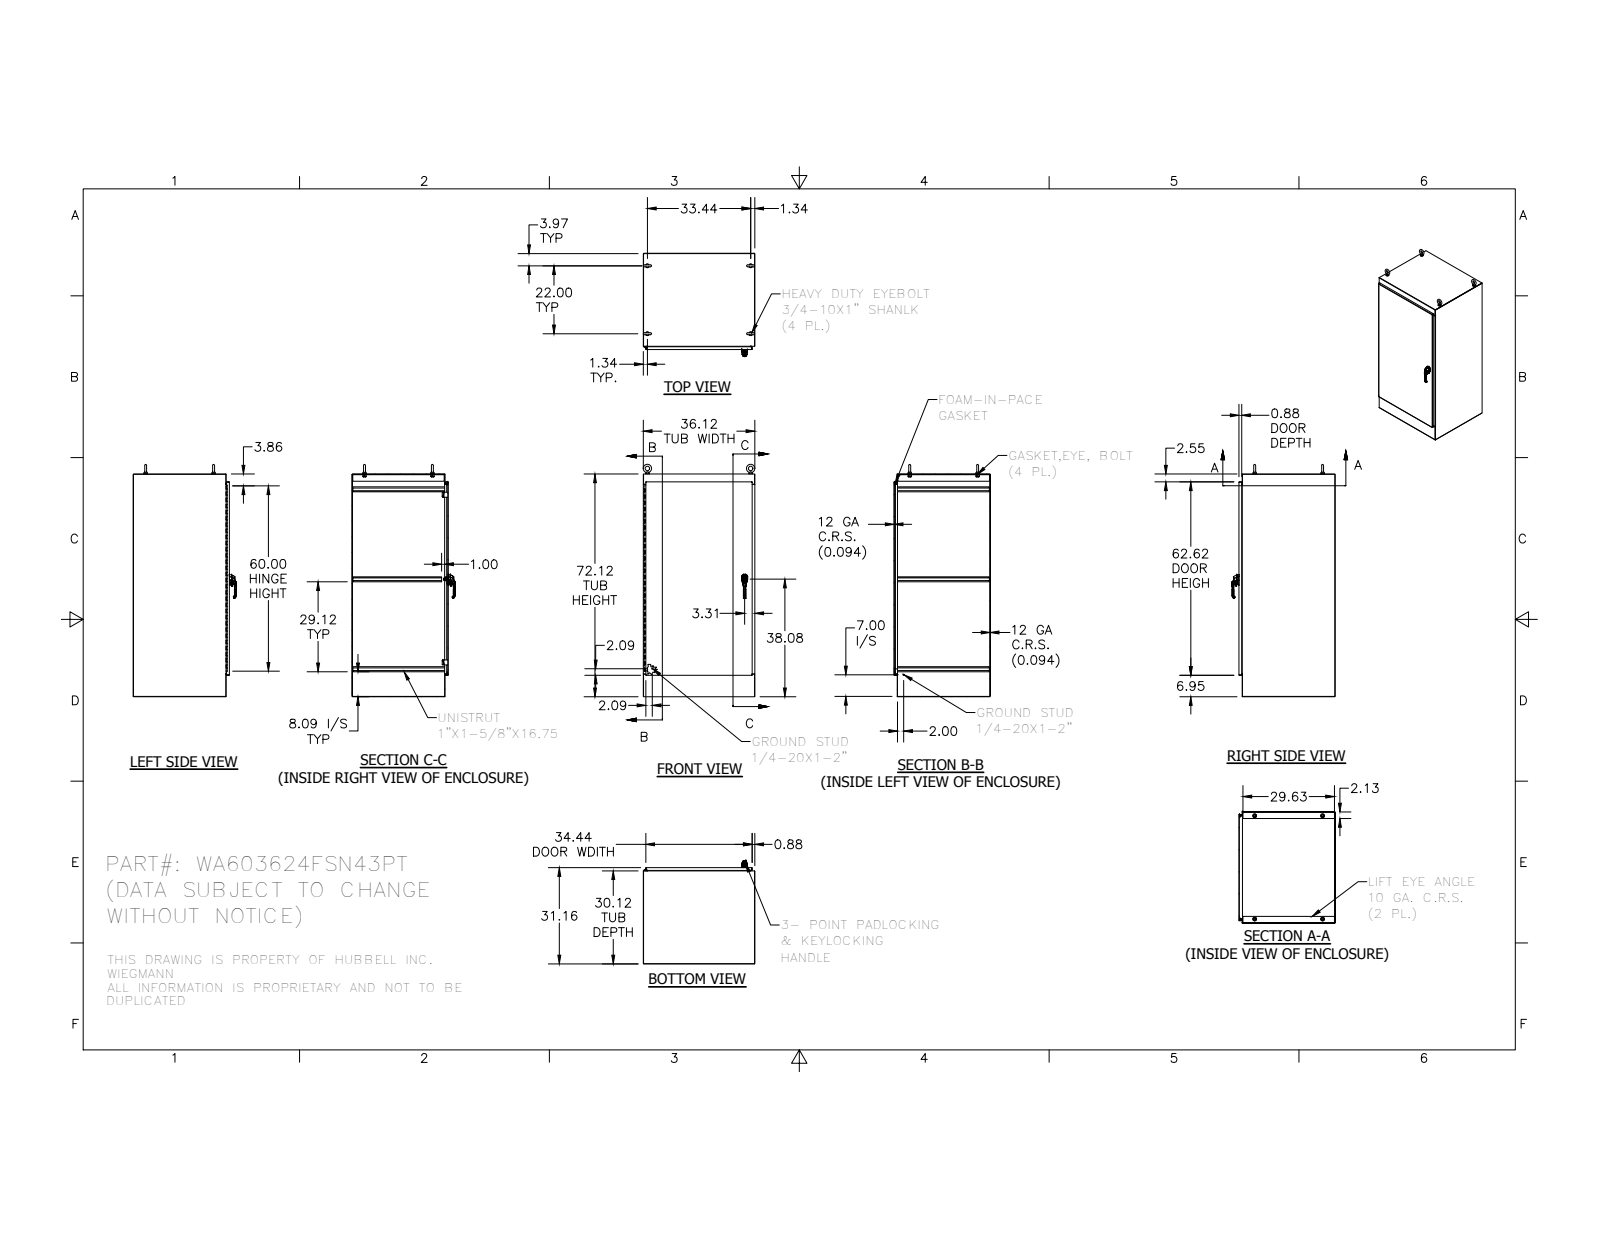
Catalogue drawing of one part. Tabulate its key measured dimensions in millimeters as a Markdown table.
| quantity | value |
| --- | --- |
| part name | WA7236FSN43PT-FIP; HFW3681; HSSN1300W60T; LARGE_DOOR_ROD_ASSM-37029 (+8 more) |
| STEP written by | SolidWorks 2014 (AUTOMOTIVE_DESIGN) |
| units | millimeters |
| bodies | 59 solids, 2236 faces (862 planar, 844 cylindrical, 530 other) |
| overall size | 1911.3 × 917.6 × 791.5 |
| volume | 21 660 000 mm³ |
| surface area | 17 640 000 mm² |
| round holes (diameter × count) | 7 × 8, 5.1 × 4, 16.3 × 4, 20.7 × 4, 7.1 × 3, 6.1 × 2, 6.4 × 2, 6.4 × 2, 10.2 × 2, 10.3 × 2, 11.4 × 2, 3.2 × 1 |
| round bosses / shafts (diameter × count) | 31.8 × 4, 28.4 × 4, 19.1 × 4, 6.4 × 3, 25.4 × 2, 14.3 × 2, 13.4 × 2, 12.7 × 2 |
| partial cylindrical surfaces (radius × count) | 0.3 × 16, 0.8 × 15, 1.3 × 14, 3.2 × 13, 0.5 × 12, 1.3 × 12, 2.2 × 12, 3.2 × 12 |
| main face-to-face distances | 2.4, 789.1, 915.2, 912.8, 786.7, 917.6, 1829.6, 791.5, 1827.2, 1832 |
| hole center spacings | 1370.2, 1389.3, 19.4, 19.4, 30.4, 32.3, 558.8, 849.3 |
